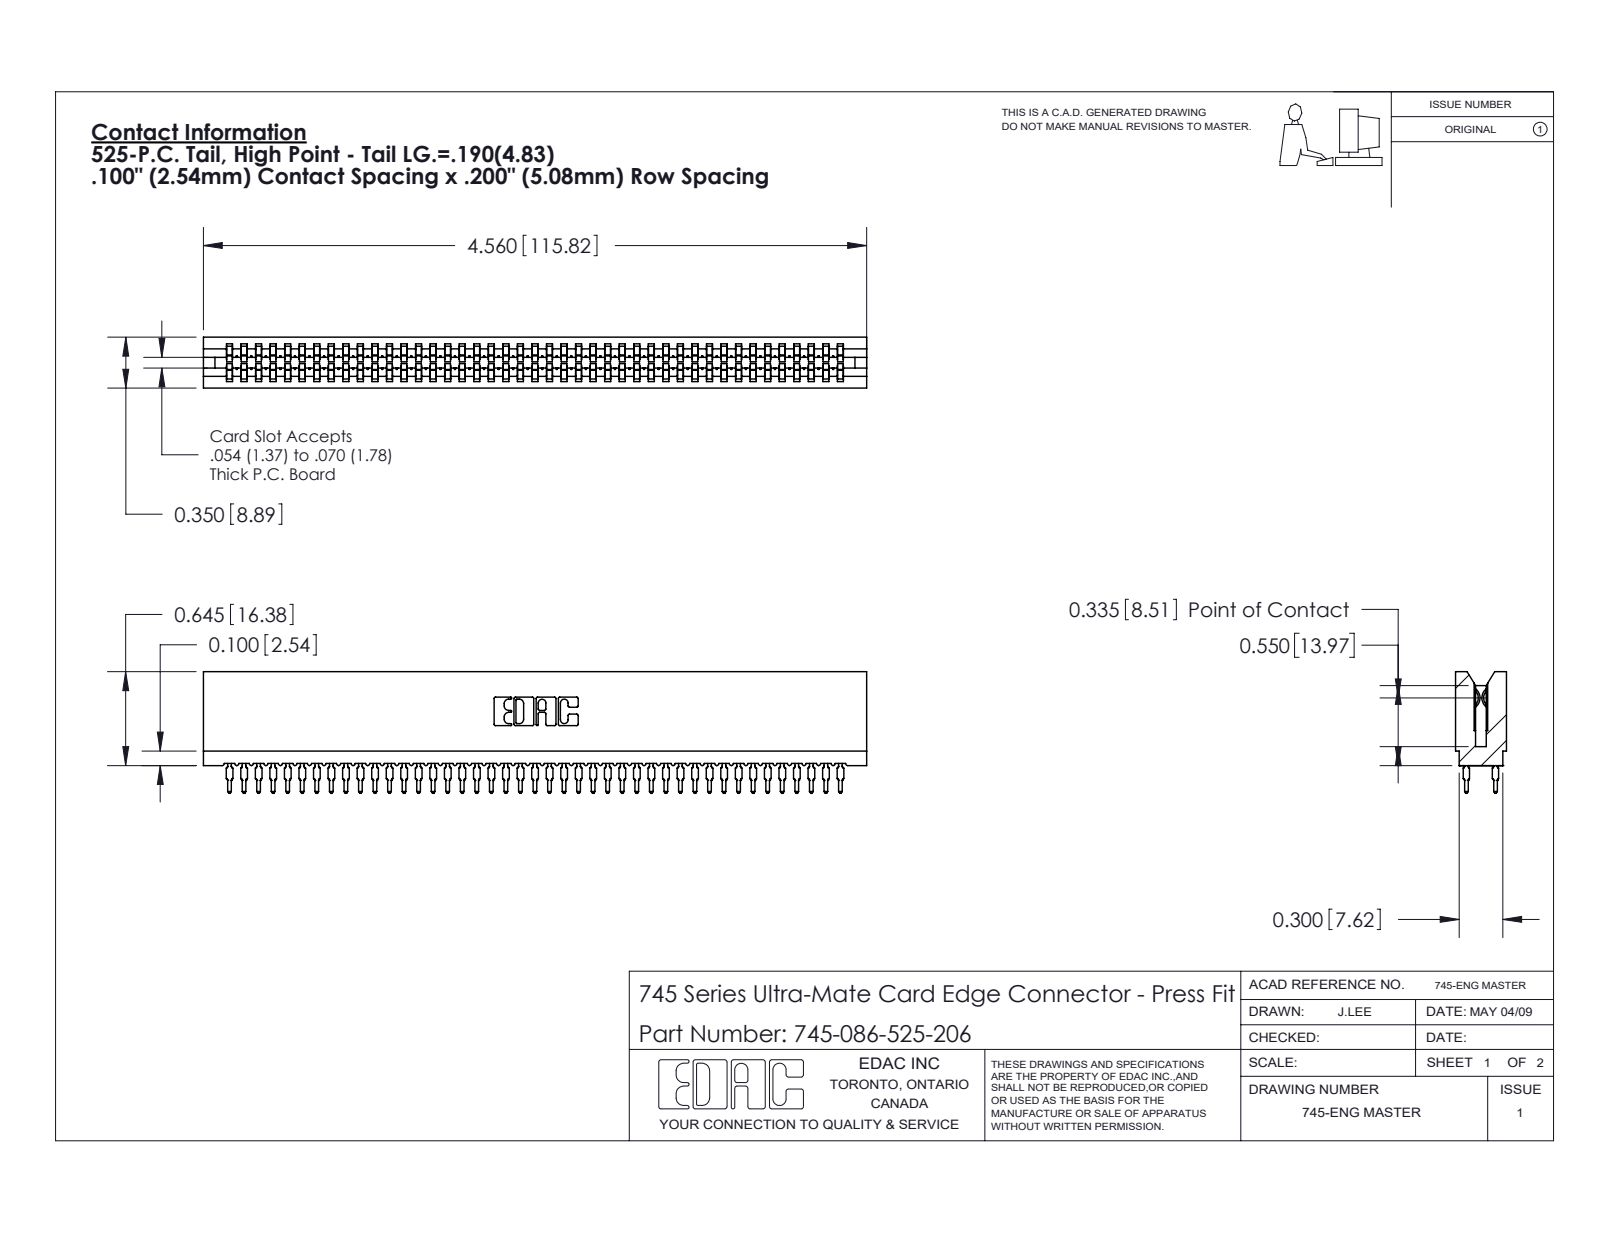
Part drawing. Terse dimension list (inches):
name: 745 Part_Insulator Option - 06; 745-292-001_525; 745-086-525-206
written by: SolidWorks 2020 (CONFIG_CONTROL_DESIGN)
unit: in
bodies: 87 solids, 7793 faces (4012 planar, 1545 cylindrical, 2236 other)
size: 4.56 × 0.836 × 0.35
volume: 0.633 in³; area: 32.66 in²
rounds: 172× R0.021, 86× R0.015, 22× R0.01, 8× R0.005, 8× R0.011, 6× R0.007, 6× R0.031, 3× R0.026
face distances: 0.35, 0.063, 0.287, 0.045, 0.305, 0.018, 0.243, 0.138, 0.212, 0.093
